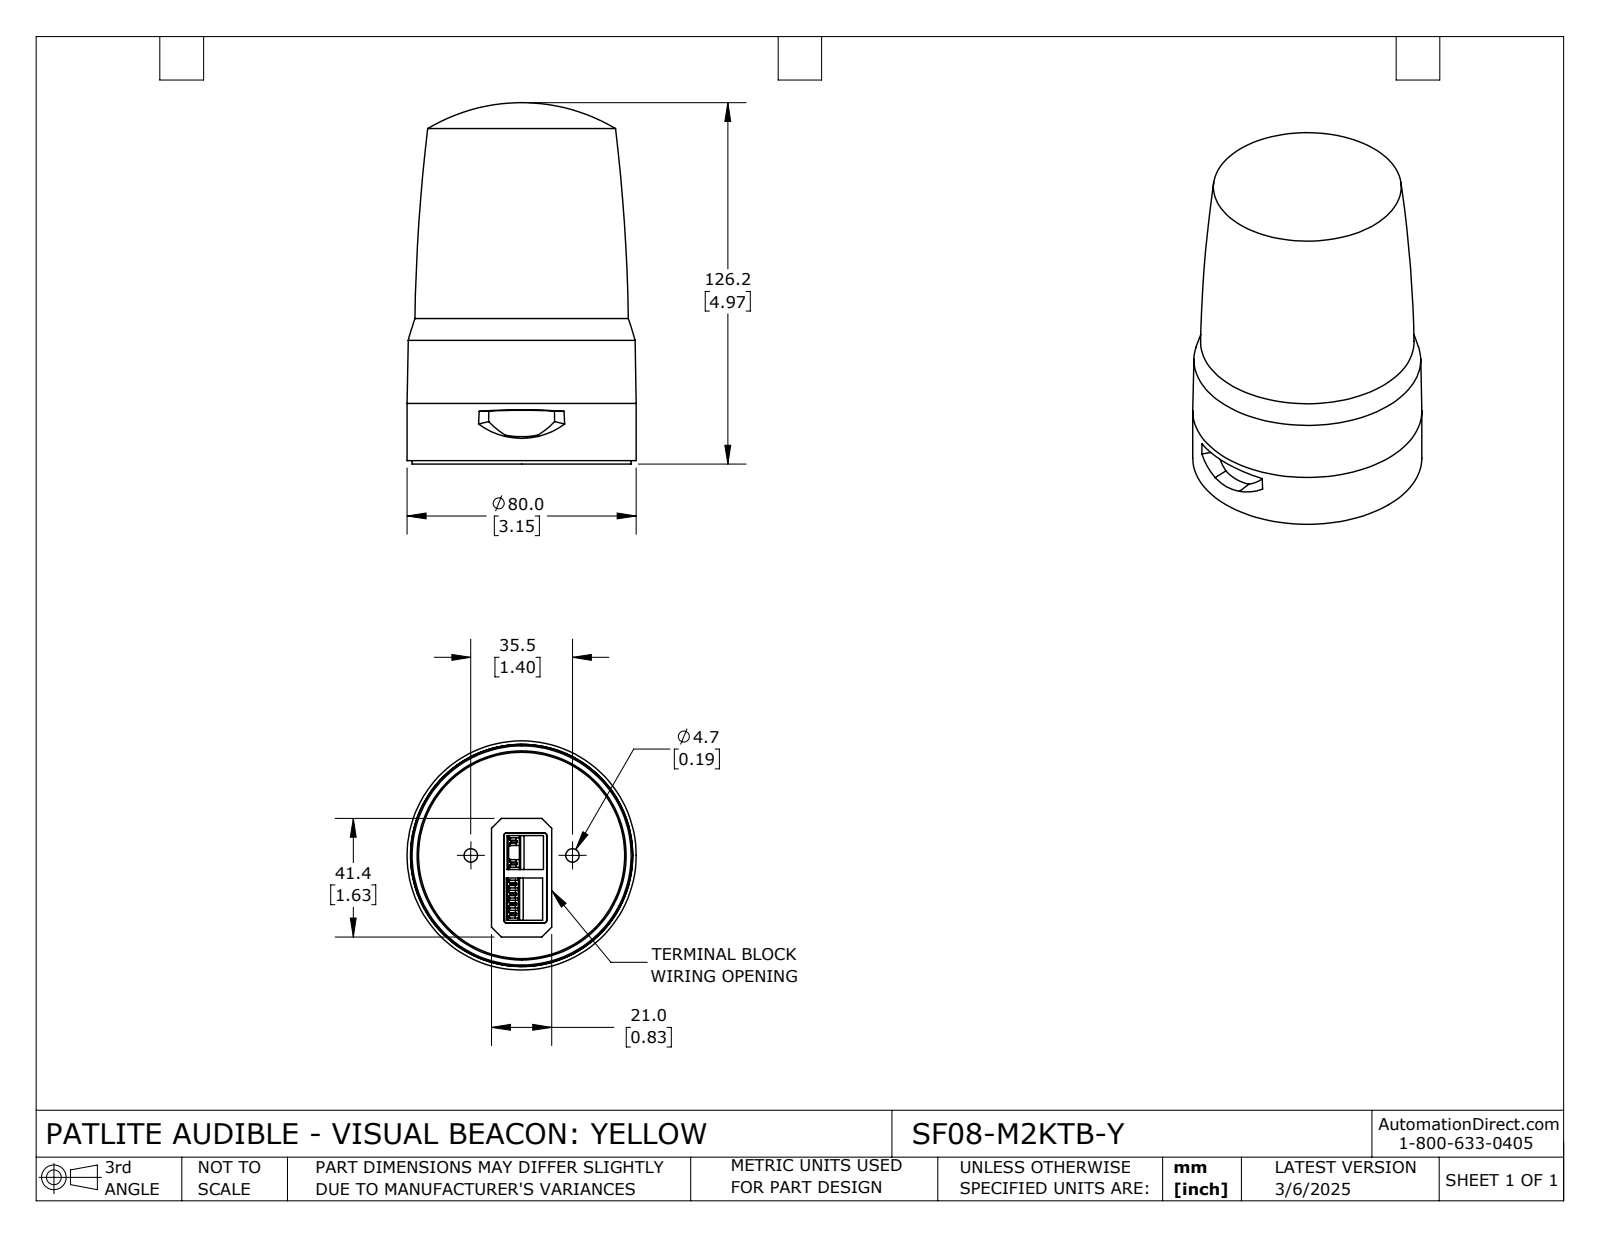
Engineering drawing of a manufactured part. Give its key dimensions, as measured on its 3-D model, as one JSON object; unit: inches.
{"part_name": "SF08-M2KTB-Y", "step_written_by": "SolidWorks 2024 (CONFIG_CONTROL_DESIGN)", "units": "inches", "bodies": {"solids": 2, "faces": 262, "planar": 168, "cylindrical": 32, "other": 62}, "overall_size": [4.969, 3.15, 3.15], "volume_in3": 29.79, "surface_area_in2": 84.61, "round_holes": [[0.185, 2], [0.48, 2], [2.874, 1]], "round_bosses_or_shafts": [[3.15, 1], [3.012, 1], [2.937, 1], [2.835, 1]], "partial_cylinders_radius": [[0.039, 4], [0.012, 2], [1.362, 1], [1.378, 1]], "face_to_face_distances": [0.618, 0.248, 0.37, 0.118, 0.201, 0.571, 0.124, 0.242, 0.051, 0.49], "hole_center_spacings": [0.699, 1.398]}
